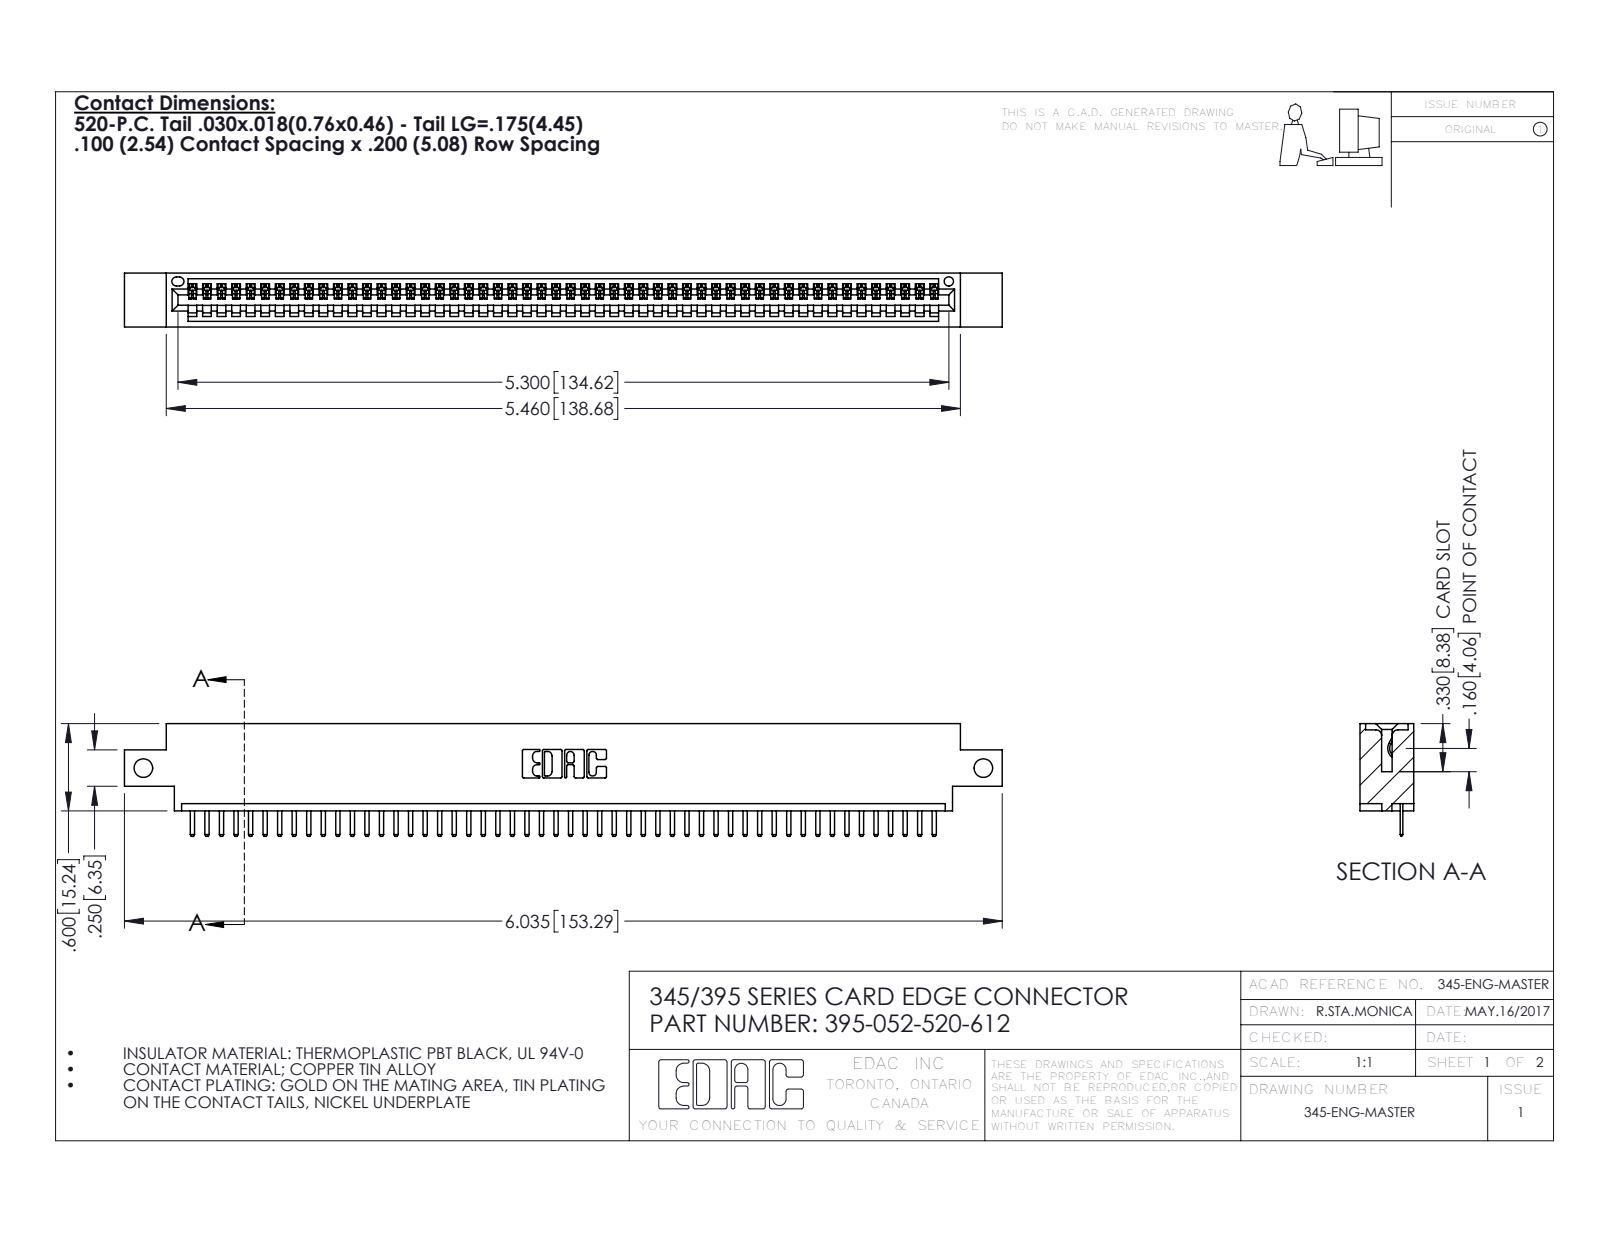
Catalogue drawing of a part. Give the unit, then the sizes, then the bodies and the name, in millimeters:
Units: millimetres
Overall size (bounding box): 153.3 × 19.7 × 9.4
Round holes (diameter × count): ⌀3.3 ×2, ⌀1.6 ×1
Partial cylindrical surfaces — rounded edges, fillets, slot ends (radius × count): R0.3 ×106, R0.2 ×104, R0.3 ×22, R0.2 ×6, R0.8 ×6, R0.7 ×3, R0.8 ×2, R1 ×2
Main face-to-face distances: 7.6, 1.8, 9.4, 5.1, 2.5, 6.9, 0.6, 5.7, 1.8, 4.4
Hole centre spacings: 146.7
Volume: 14 300 mm³ · Surface area: 18 630 mm²
Bodies: 53 solids, 3354 faces (2268 planar, 1086 cylindrical, 0 other)
Part name (STEP PRODUCT): 345 Part_0.170 Offset - Side Mount; 345-292-001_345-293-120; 395-052-520-612
STEP written by: SolidWorks 2016 (CONFIG_CONTROL_DESIGN)
